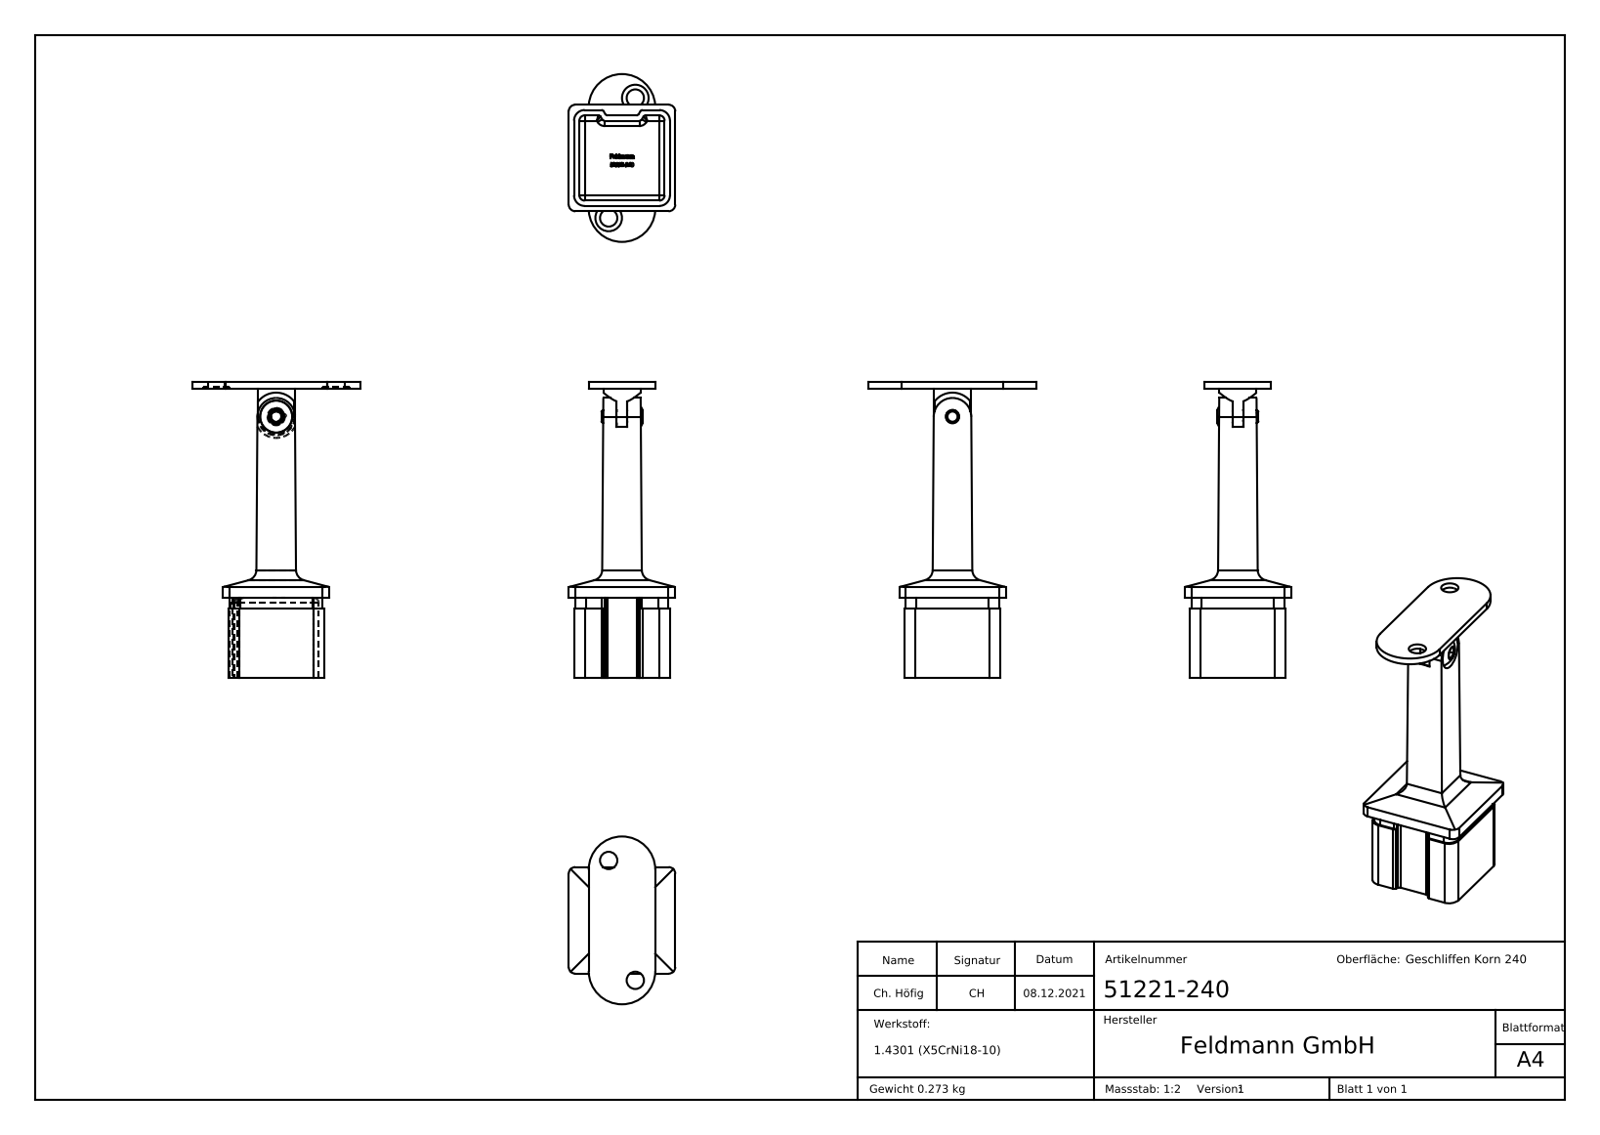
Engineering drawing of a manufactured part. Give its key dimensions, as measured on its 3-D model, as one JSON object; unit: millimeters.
{"part_name": "51221-240 Teil3; 51221-240; 51221-240 Teil1_51221-240 Teil1; 51221-240 Teil1 (+3 more)", "step_written_by": "SolidWorks 2018 (CONFIG_CONTROL_DESIGN)", "units": "millimeters", "bodies": {"solids": 3, "faces": 348, "planar": 189, "cylindrical": 58, "other": 101}, "overall_size": [111, 63, 40], "volume_mm3": 34467, "surface_area_mm2": 20299, "round_holes": [[6.5, 3], [10, 2], [5, 1], [6.2, 1], [12.1, 1]], "round_bosses_or_shafts": [[14, 1], [12, 1], [4.77, 1]], "partial_cylinders_radius": [[4, 12], [2, 11], [1, 10], [2.5, 4], [12.5, 2], [7.05, 1], [8, 1], [8.5, 1]], "face_to_face_distances": [2, 34, 32, 36, 2.5, 81, 78.5, 4, 30, 18], "hole_center_spacings": [46.1]}
